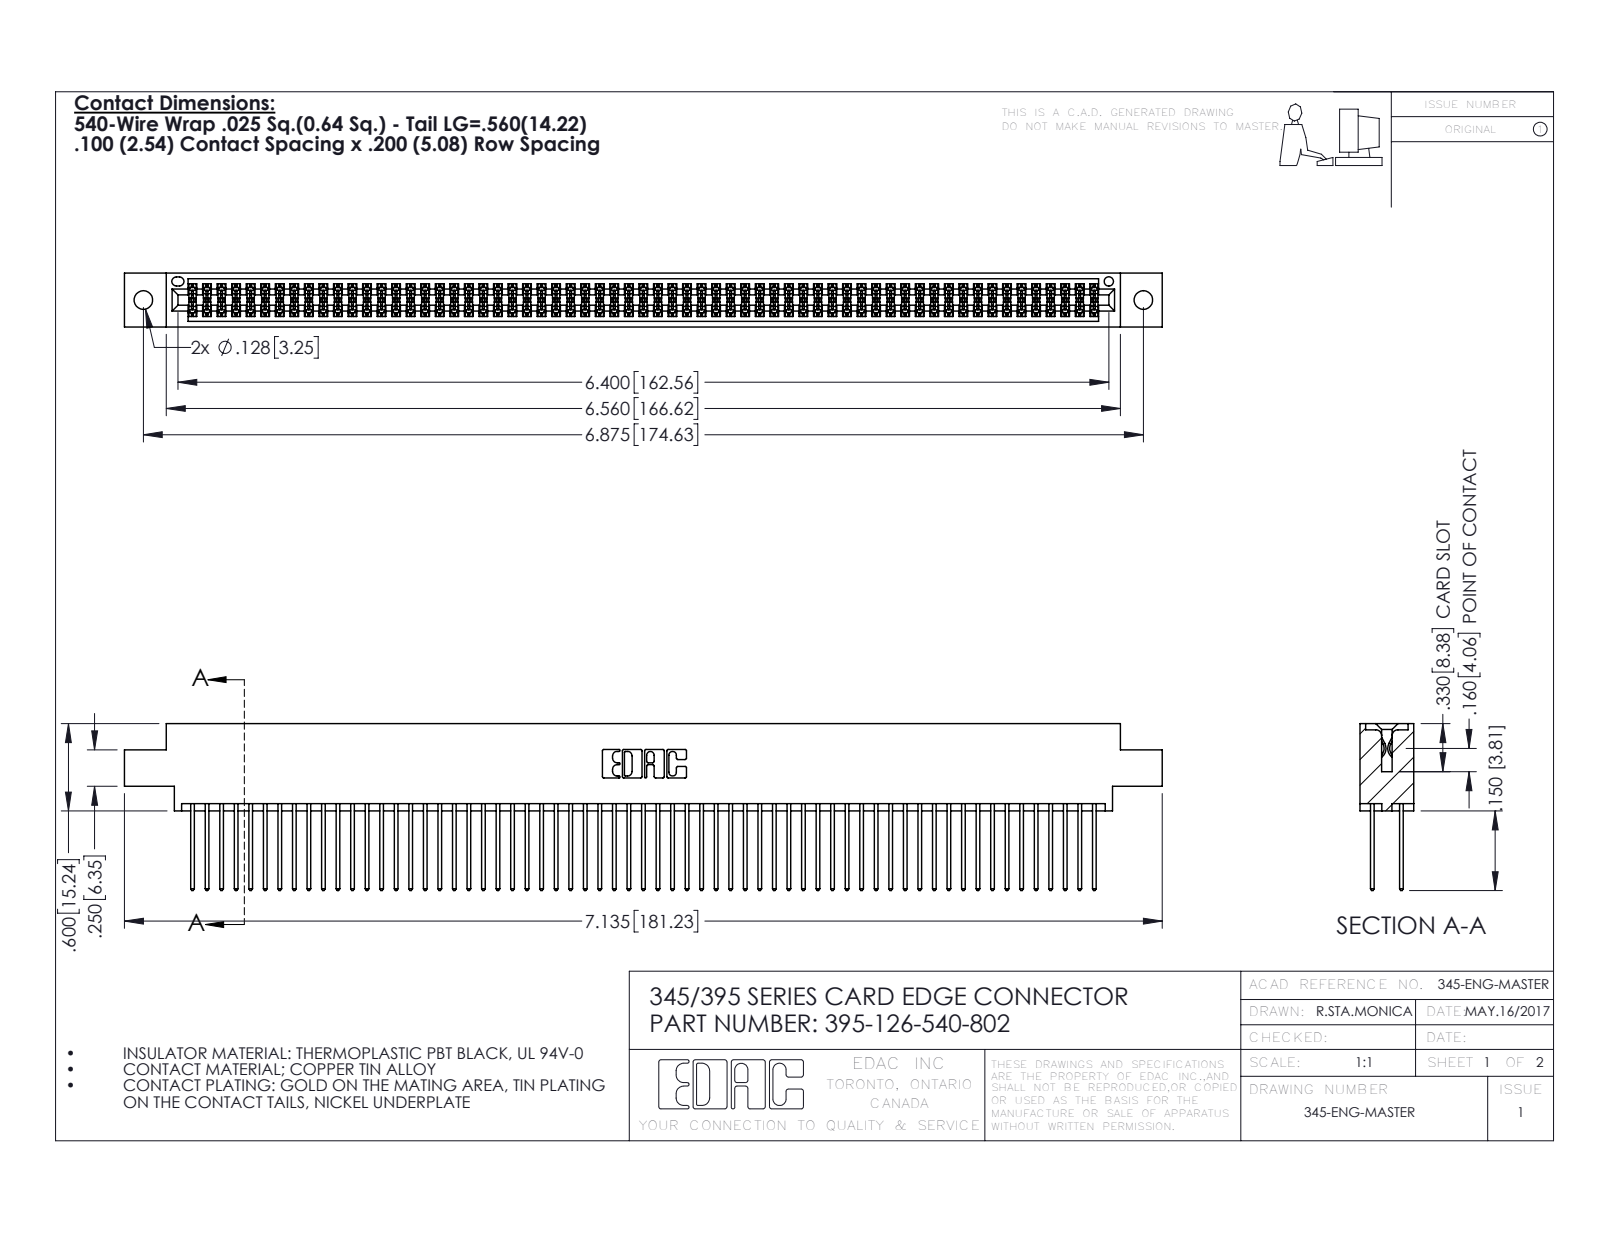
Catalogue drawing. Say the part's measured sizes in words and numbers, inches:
The part is named "395-126-540-802; 345-292-001_345-293-140; 345 Part_0.170 Offset - 0.128 Dia". Its 3-D file was written by "SolidWorks 2016 (CONFIG_CONTROL_DESIGN)". It is 127 solids with 6430 faces: 4242 planar, 2188 cylindrical and 0 other. Overall it measures 7.135 by 1.147 by 0.37 inches. Its volume is 1.106 cubic inches and its surface area 45.4 square inches. Round holes: 2 of diameter 0.128, 1 of diameter 0.064. Partial cylindrical surfaces (rounded edges, fillets, slot ends): 189 of radius 0.006, 126 of radius 0.01, 22 of radius 0.01, 6 of radius 0.007, 6 of radius 0.031, 3 of radius 0.026, 2 of radius 0.014, 2 of radius 0.019. The main face-to-face distances are 0.072, 0.298, 0.2, 0.098, 0.272, 0.025, 0.37, 0.225, 0.175, 0.149. The hole center spacings are 0.27, 6.639, 6.875.
